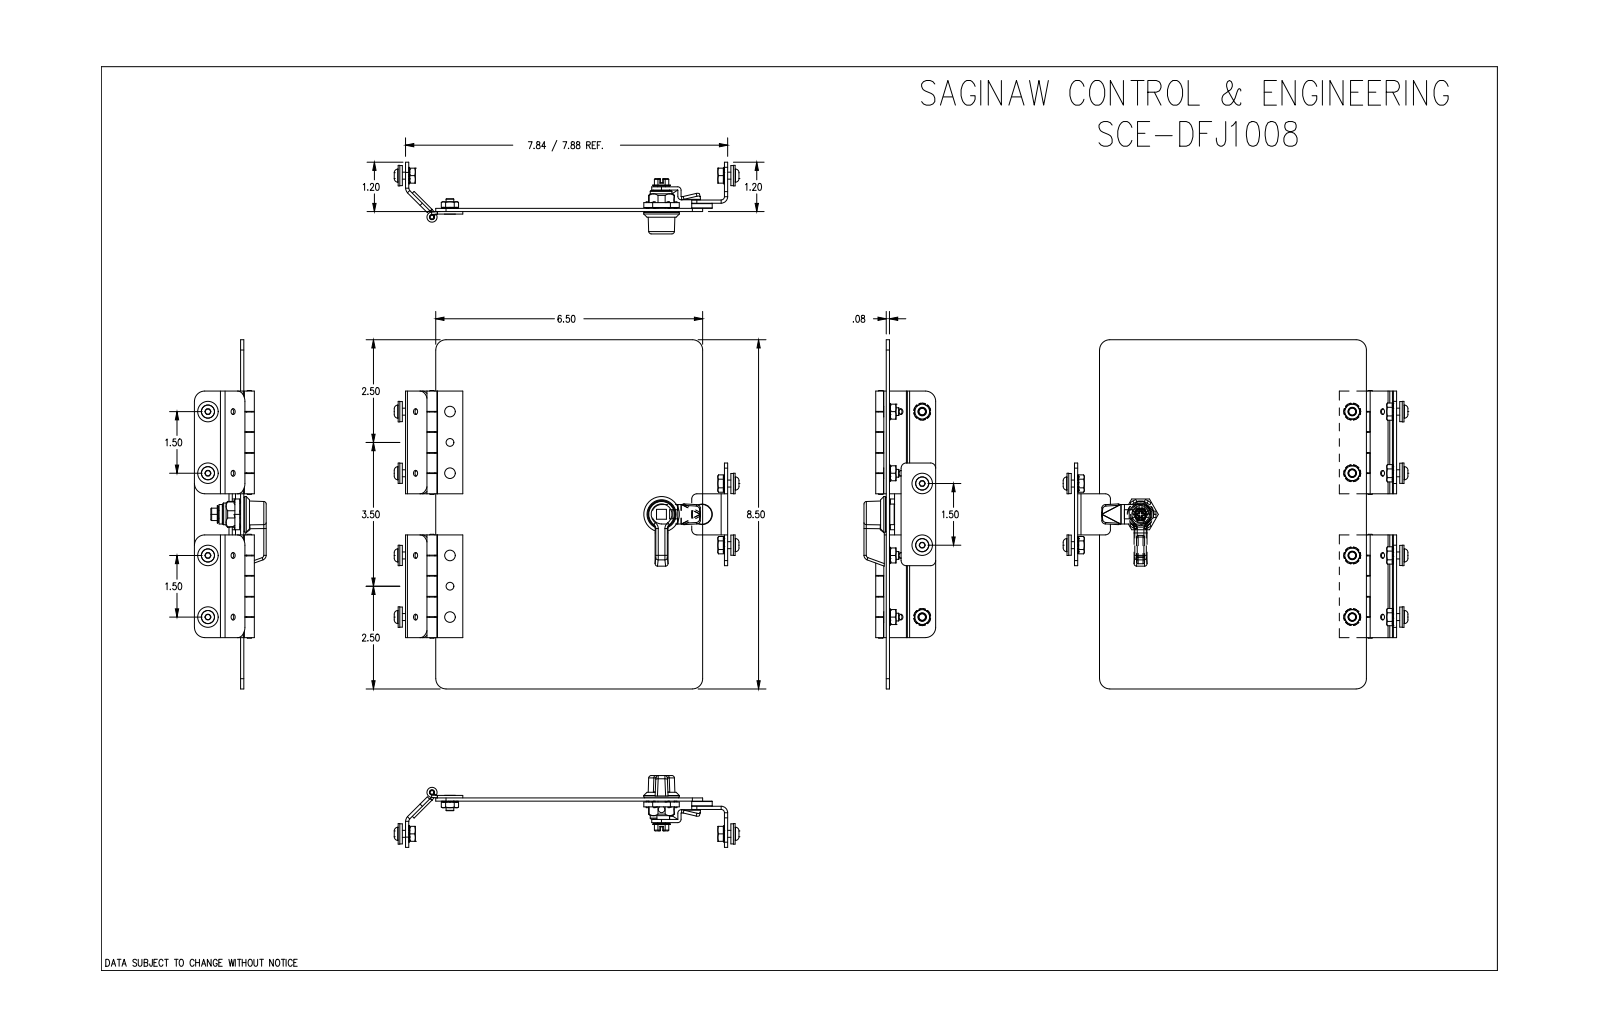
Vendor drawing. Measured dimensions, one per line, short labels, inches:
name: SCE-DFJ1008
written by: SolidWorks 2021 (AUTOMOTIVE_DESIGN)
unit: in
bodies: 46 solids, 1380 faces (962 planar, 202 cylindrical, 216 other)
size: 8.5 × 8.396 × 1.746
volume: 6.423 in³; area: 179.7 in²
holes: 10× ⌀0.19, 10× ⌀0.25, 6× ⌀0.249, 4× ⌀0.136, 4× ⌀0.142, 4× ⌀0.193, 3× ⌀0.157, 2× ⌀0.188, 1× ⌀0.071, 1× ⌀0.125, 1× ⌀0.144, 1× ⌀0.398
bosses: 7× ⌀0.5, 6× ⌀0.49, 6× ⌀0.17, 4× ⌀0.256, 4× ⌀0.188, 1× ⌀0.866, 1× ⌀0.827, 1× ⌀0.551
rounds: 18× R0.125, 12× R0.25, 8× R0.039, 4× R0.004, 4× R0.059, 4× R0.083, 3× R0.118, 2× R0.03
face distances: 0.078, 0.06, 0.138, 7.766, 7.844, 7.688, 0.203, 0.125, 0.263, 1
hole spacings: 1.5, 3.5, 0.75, 1.75, 2, 5, 0.25, 0.949
